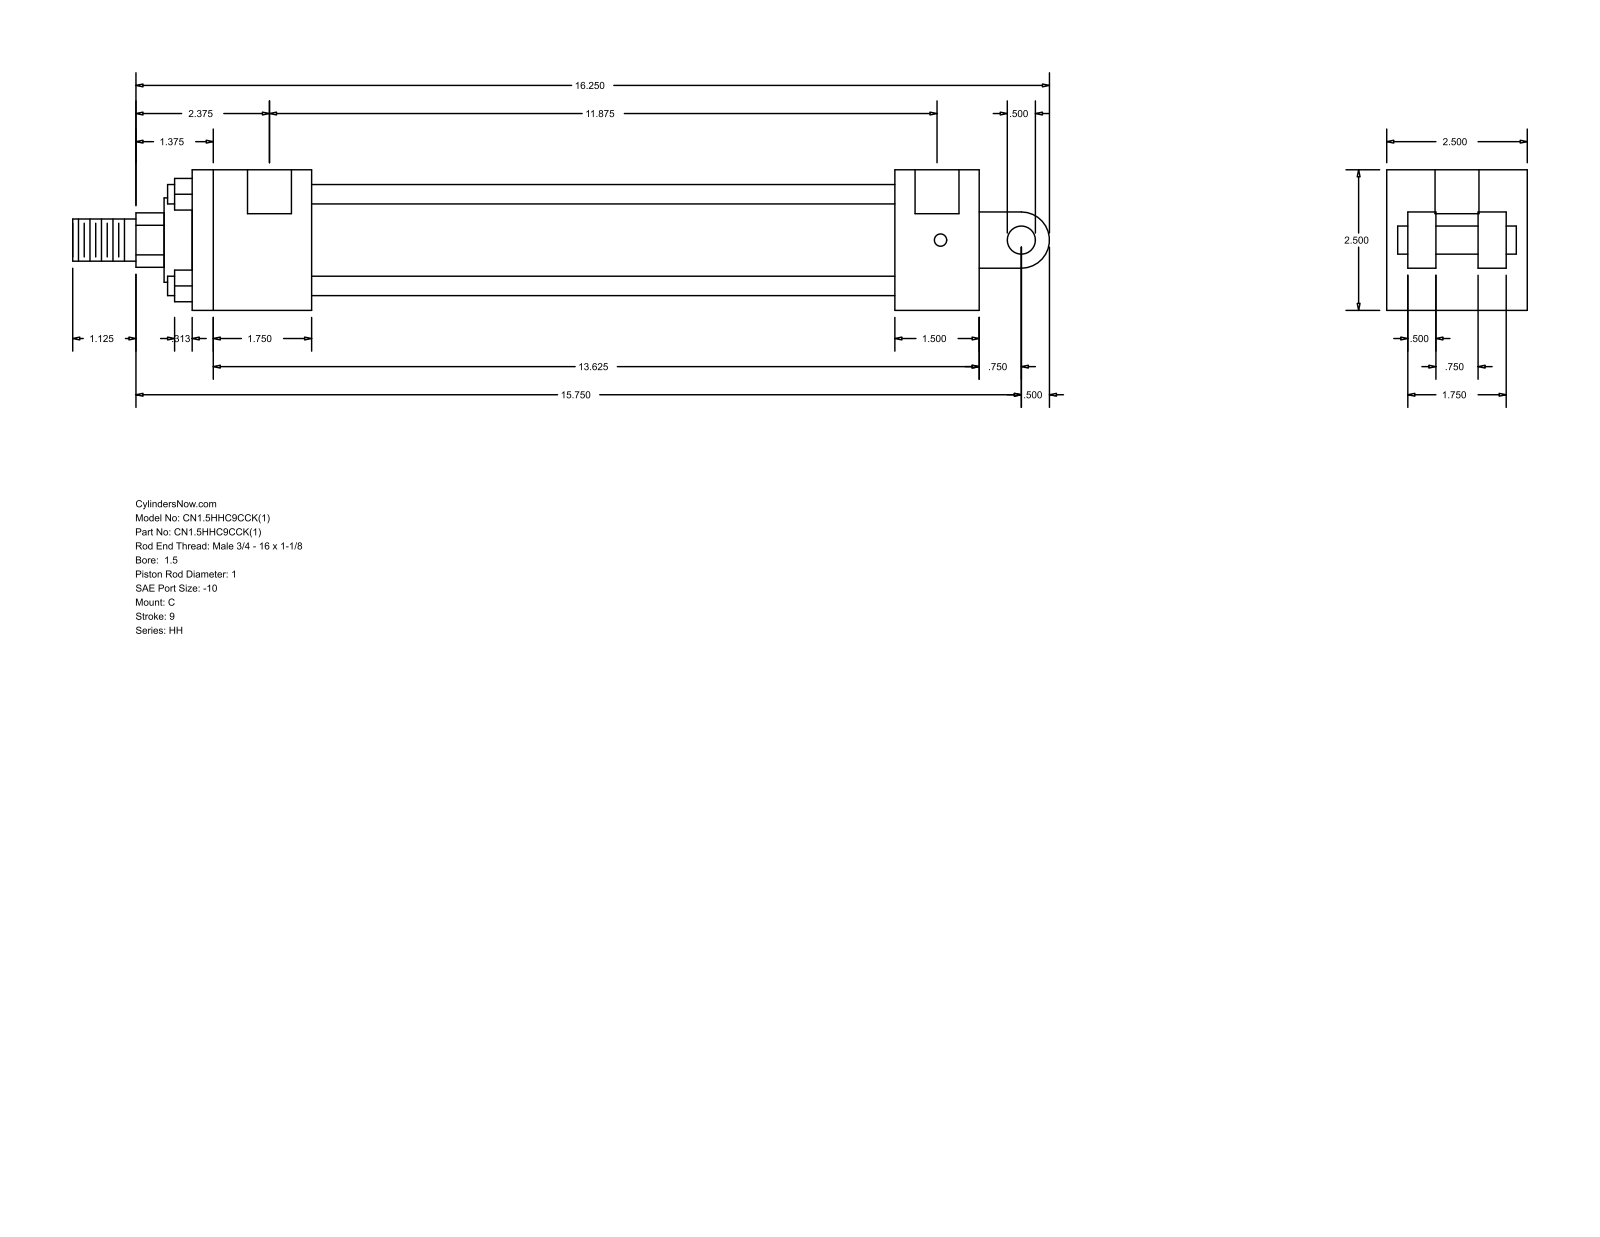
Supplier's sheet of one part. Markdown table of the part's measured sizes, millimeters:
| quantity | value |
| --- | --- |
| part name | HH_C__0150_1 |
| STEP written by | GSSL Pune (CONFIG_CONTROL_DESIGN) |
| units | millimeters |
| bodies | 0 solids, 99 faces (70 planar, 29 cylindrical, 0 other) |
| overall size | 441.32 × 63.5 × 63.5 |
| round holes (diameter × count) | 5.56 × 4, 19.84 × 2 |
| round bosses / shafts (diameter × count) | 8.76 × 4, 44.45 × 1, 38.1 × 1, 25.4 × 1, 19.05 × 1, 12.7 × 1 |
| partial cylindrical surfaces (radius × count) | 12.29 × 1, 12.7 × 1 |
| main face-to-face distances | 63.5, 53.98, 38.1, 263.52, 301.62, 317.5, 355.6, 12.7, 22.22, 41.28 |
| hole center spacings | 1.59, 303.21, 304.8, 301.62 |
